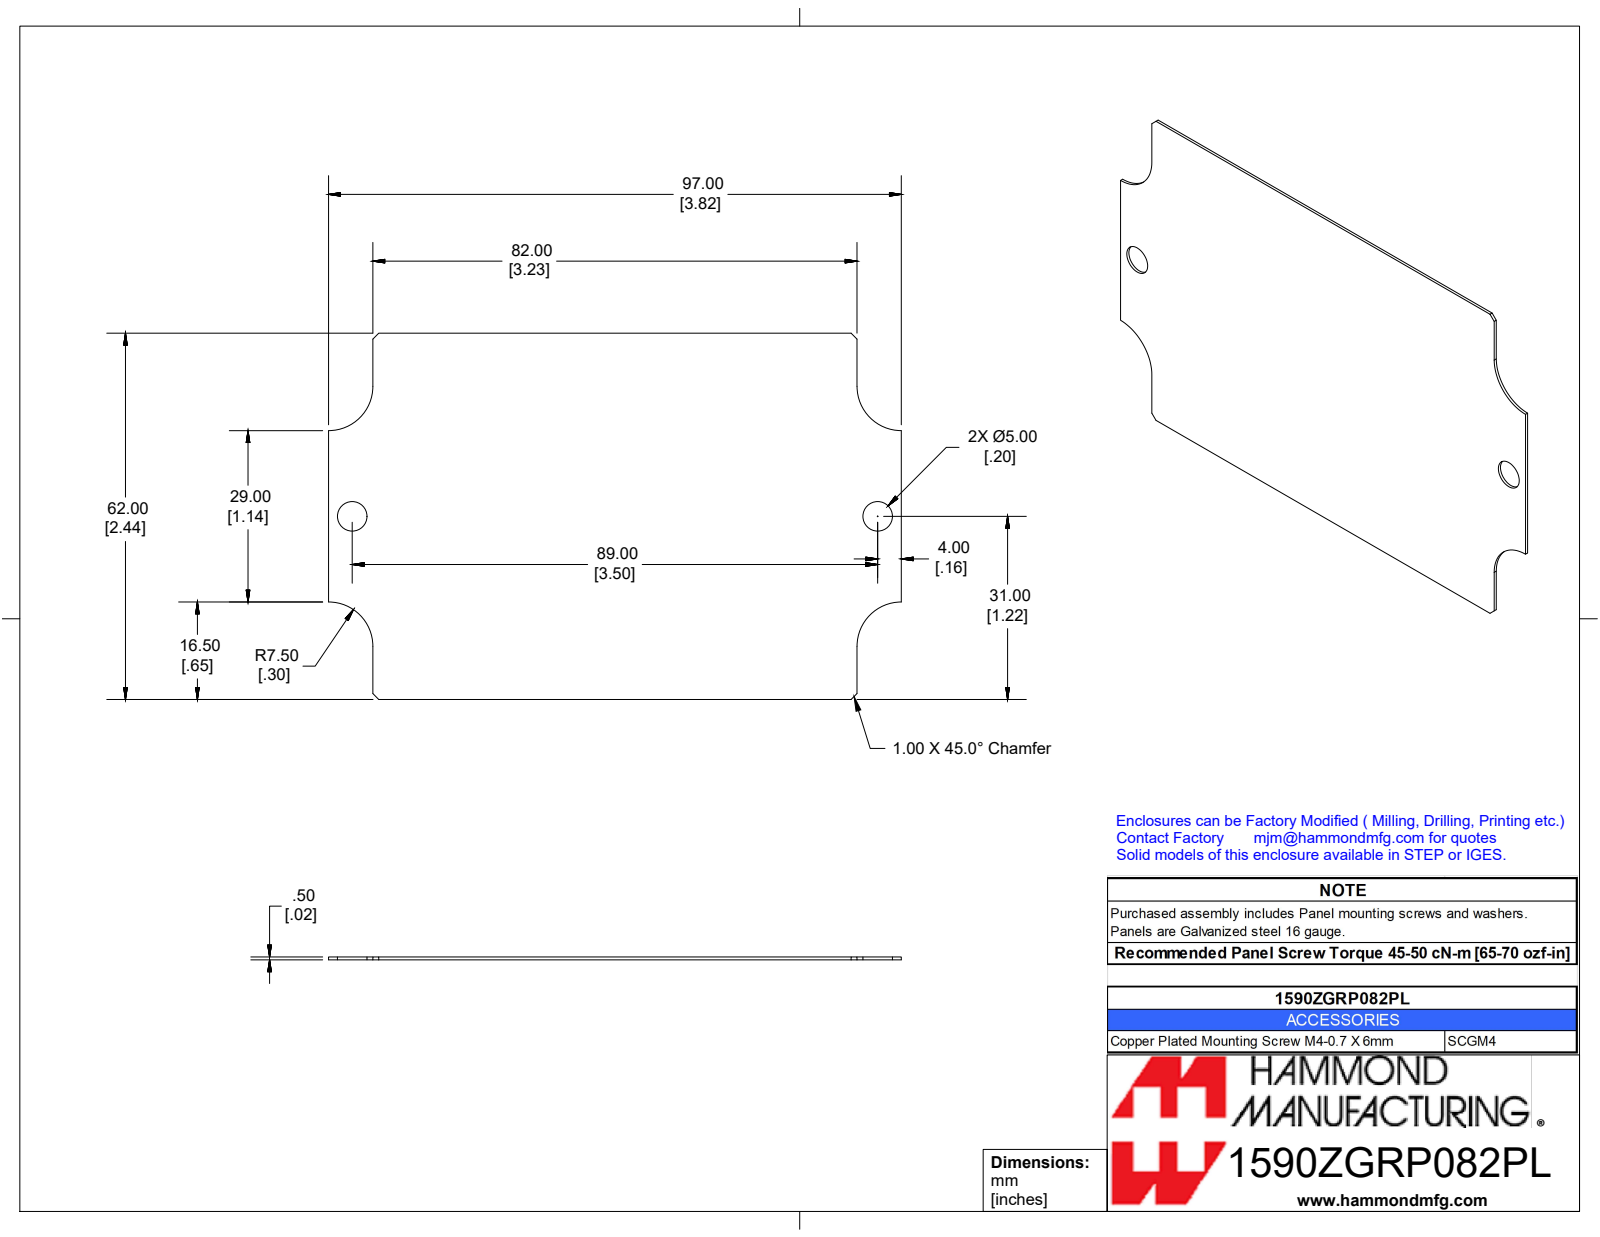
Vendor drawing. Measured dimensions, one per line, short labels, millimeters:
name: 1590ZGRP082PL
written by: SolidWorks 2019 (CONFIG_CONTROL_DESIGN)
unit: mm
bodies: 1 solid, 20 faces (14 planar, 6 cylindrical, 0 other)
size: 97 × 62 × 0.5
volume: 2 770 mm³; area: 11 220 mm²
holes: 2× ⌀5
rounds: 4× R7.5
face distances: 0.5, 62, 7.5, 89.5, 97, 82, 100.4
hole spacings: 89
